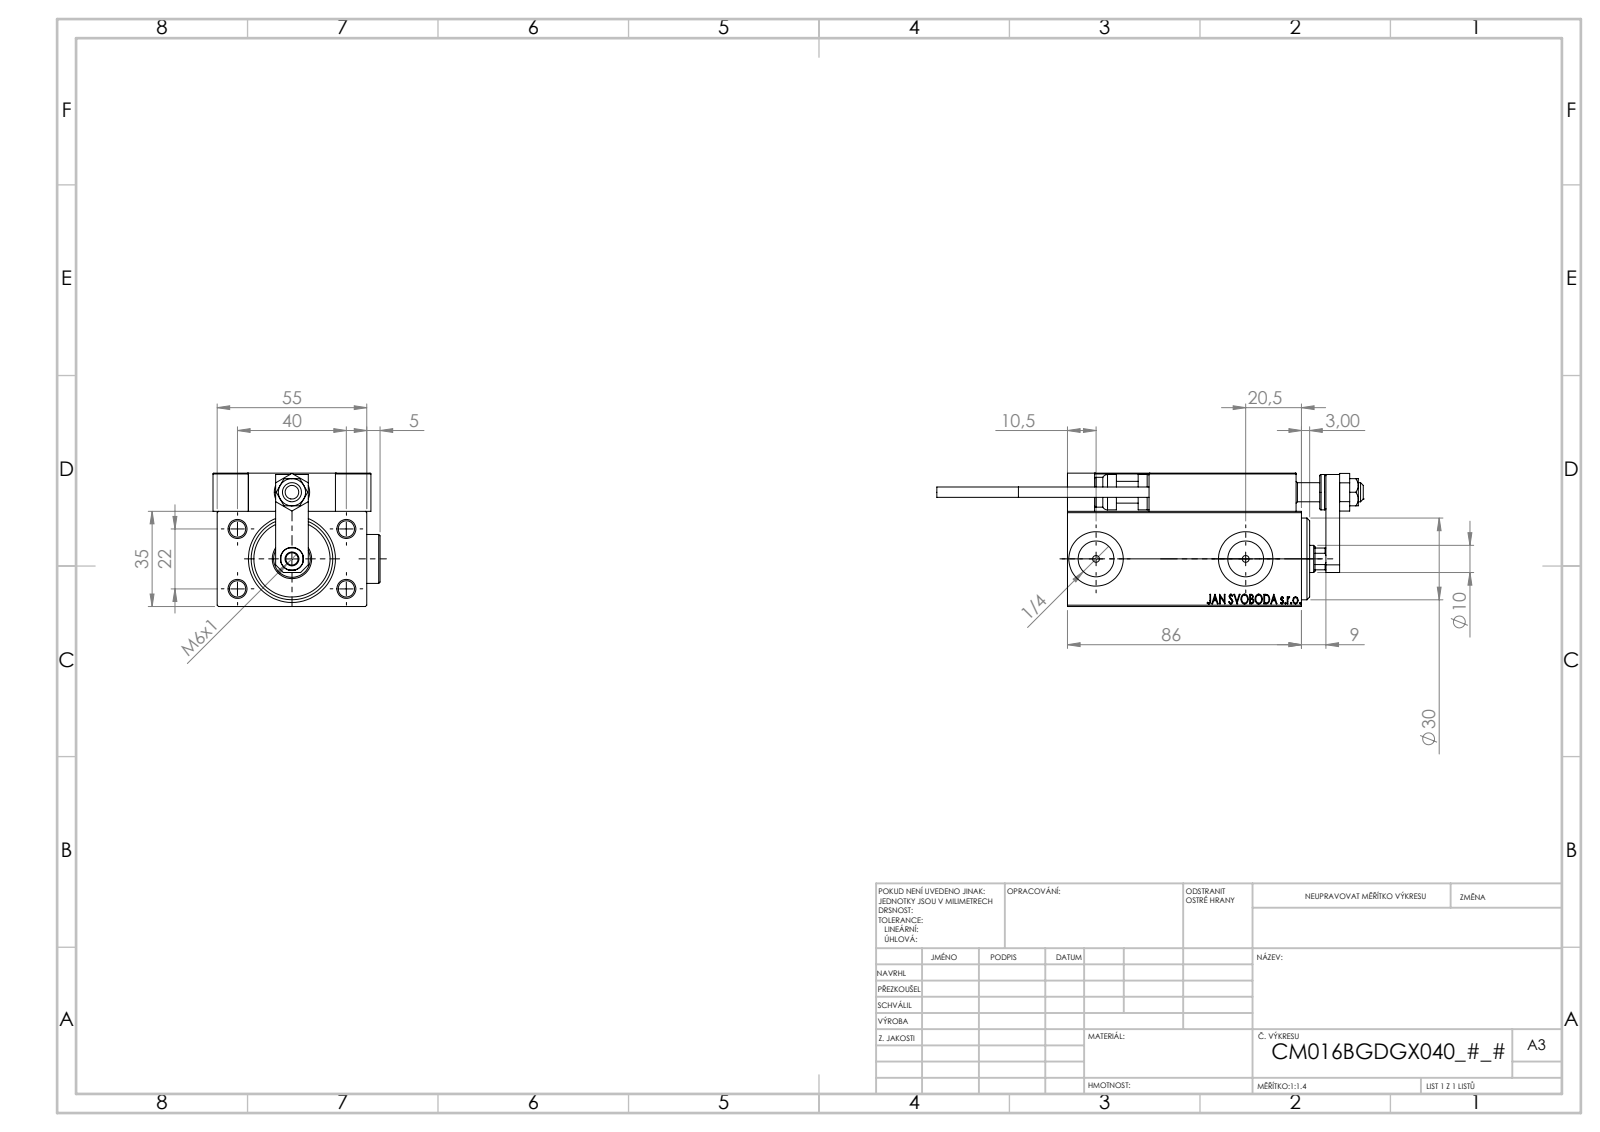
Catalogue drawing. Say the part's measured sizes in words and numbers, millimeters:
The part is named "SWITCH DIM B,W; ALLEN BOLT D8; V450CM_VC_B; ZARAZKA (+8 more)". Its 3-D file was written by "SolidWorks 2019 (CONFIG_CONTROL_DESIGN)". It is 26 solids with 1372 faces: 595 planar, 200 cylindrical and 577 other. Overall it measures 156.7 by 61.4 by 49 millimeters. Its volume is 198 353 cubic millimeters and its surface area 58 029 square millimeters. Round holes: 5 of diameter 8, 4 of diameter 3.2, 4 of diameter 4, 4 of diameter 6, 2 of diameter 2.5, 2 of diameter 5, 2 of diameter 13.16, 2 of diameter 20, 1 of diameter 4.5, 1 of diameter 7, 1 of diameter 8.5, 1 of diameter 10. Round bosses or shafts: 2 of diameter 18, 2 of diameter 5, 2 of diameter 3.8, 1 of diameter 13, 1 of diameter 11. Partial cylindrical surfaces (rounded edges, fillets, slot ends): 30 of radius 0.3, 2 of radius 3, 1 of radius 4.5. The main face-to-face distances are 35, 14, 5, 49, 55, 3, 7, 1.5, 10, 13. The hole center spacings are 22.83, 11.37, 20, 22, 24.13, 29.59, 29.69, 36.06.
